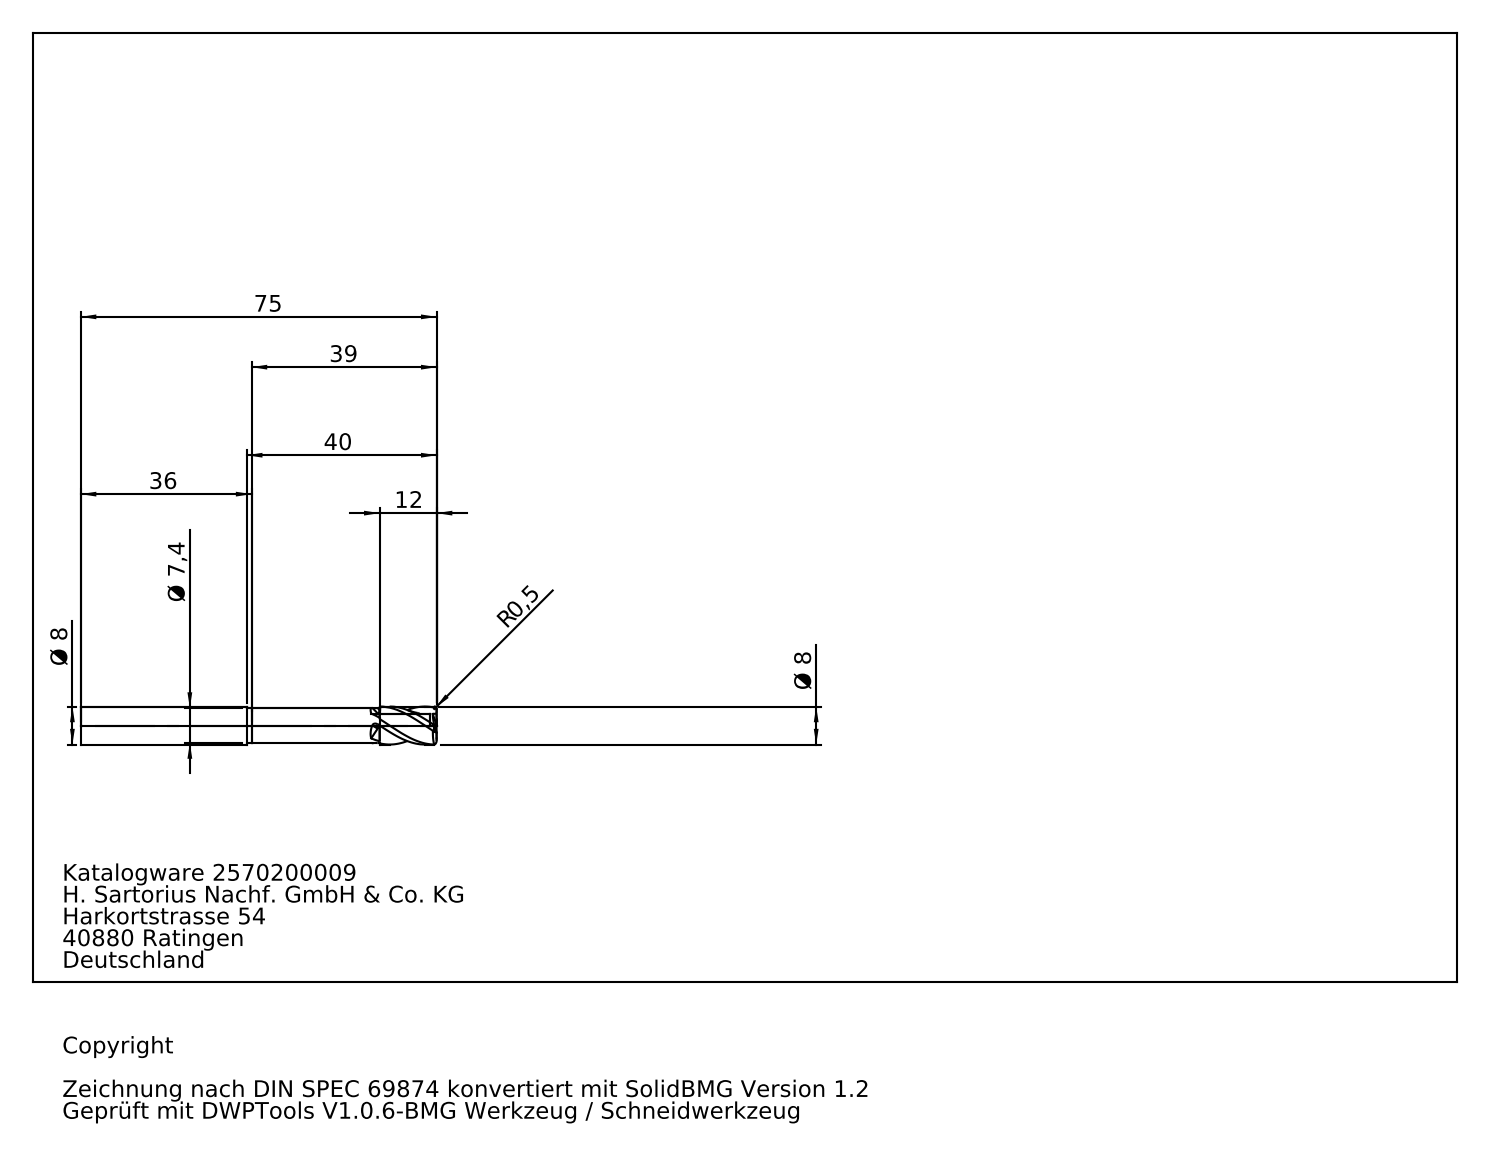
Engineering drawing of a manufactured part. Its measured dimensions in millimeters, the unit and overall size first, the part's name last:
Units: millimetres
Overall size (bounding box): 75 × 8 × 8
Round holes (diameter × count): ⌀4.8 ×1
Round bosses / shafts (diameter × count): ⌀8 ×1, ⌀7.4 ×1
Main face-to-face distances: 73.69, 63, 10.69, 35, 28, 38.69, 74.97, 39.97, 11.97, 1.28
Volume: 3 343 mm³ · Surface area: 2 336 mm²
Bodies: 2 solids, 60 faces (15 planar, 18 cylindrical, 27 other)
Part name (STEP PRODUCT): 2570200009
STEP written by: SolidWorks 2010 (AUTOMOTIVE_DESIGN)
